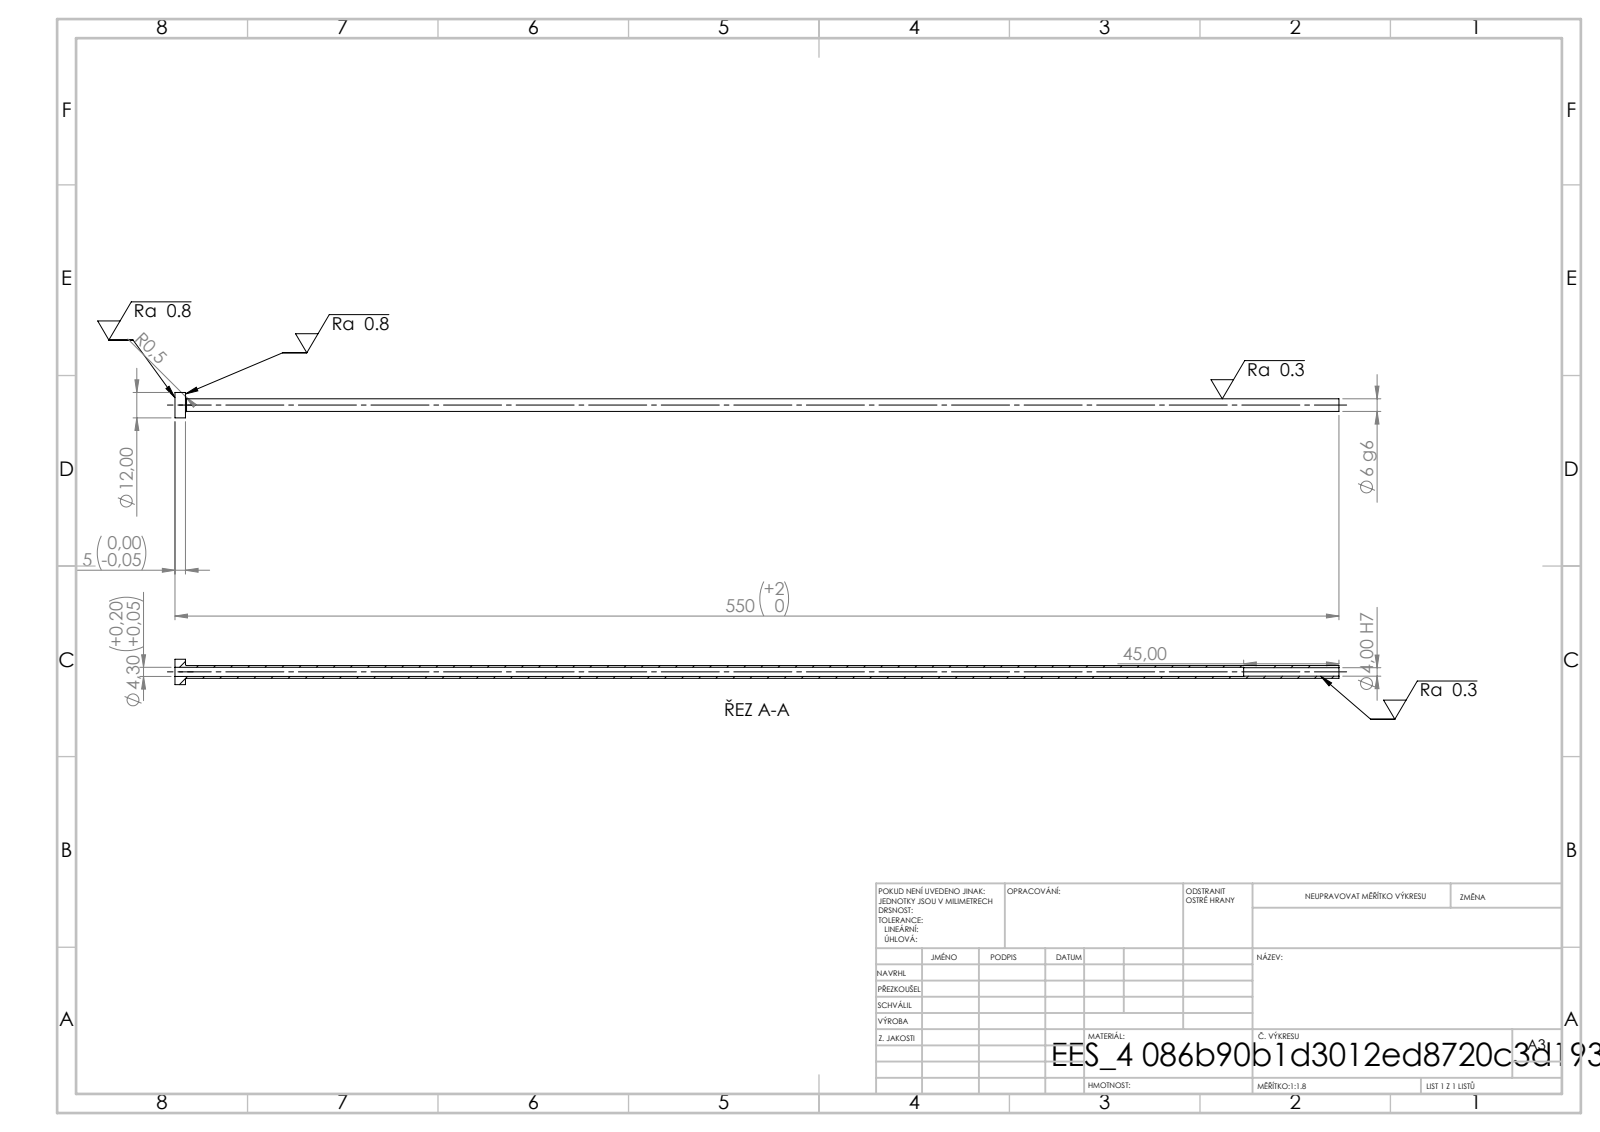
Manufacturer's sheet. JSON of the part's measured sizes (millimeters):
{"step_written_by": "SolidWorks 2019 (CONFIG_CONTROL_DESIGN)", "units": "millimeters", "bodies": {"solids": 1, "faces": 14, "planar": 4, "cylindrical": 8, "other": 2}, "overall_size": [550, 12, 12], "volume_mm3": 8077, "surface_area_mm2": 18046, "round_holes": [[4, 1], [4.3, 1]], "round_bosses_or_shafts": [[12, 1], [6, 1]], "face_to_face_distances": [5, 550, 545, 505, 500, 45]}
